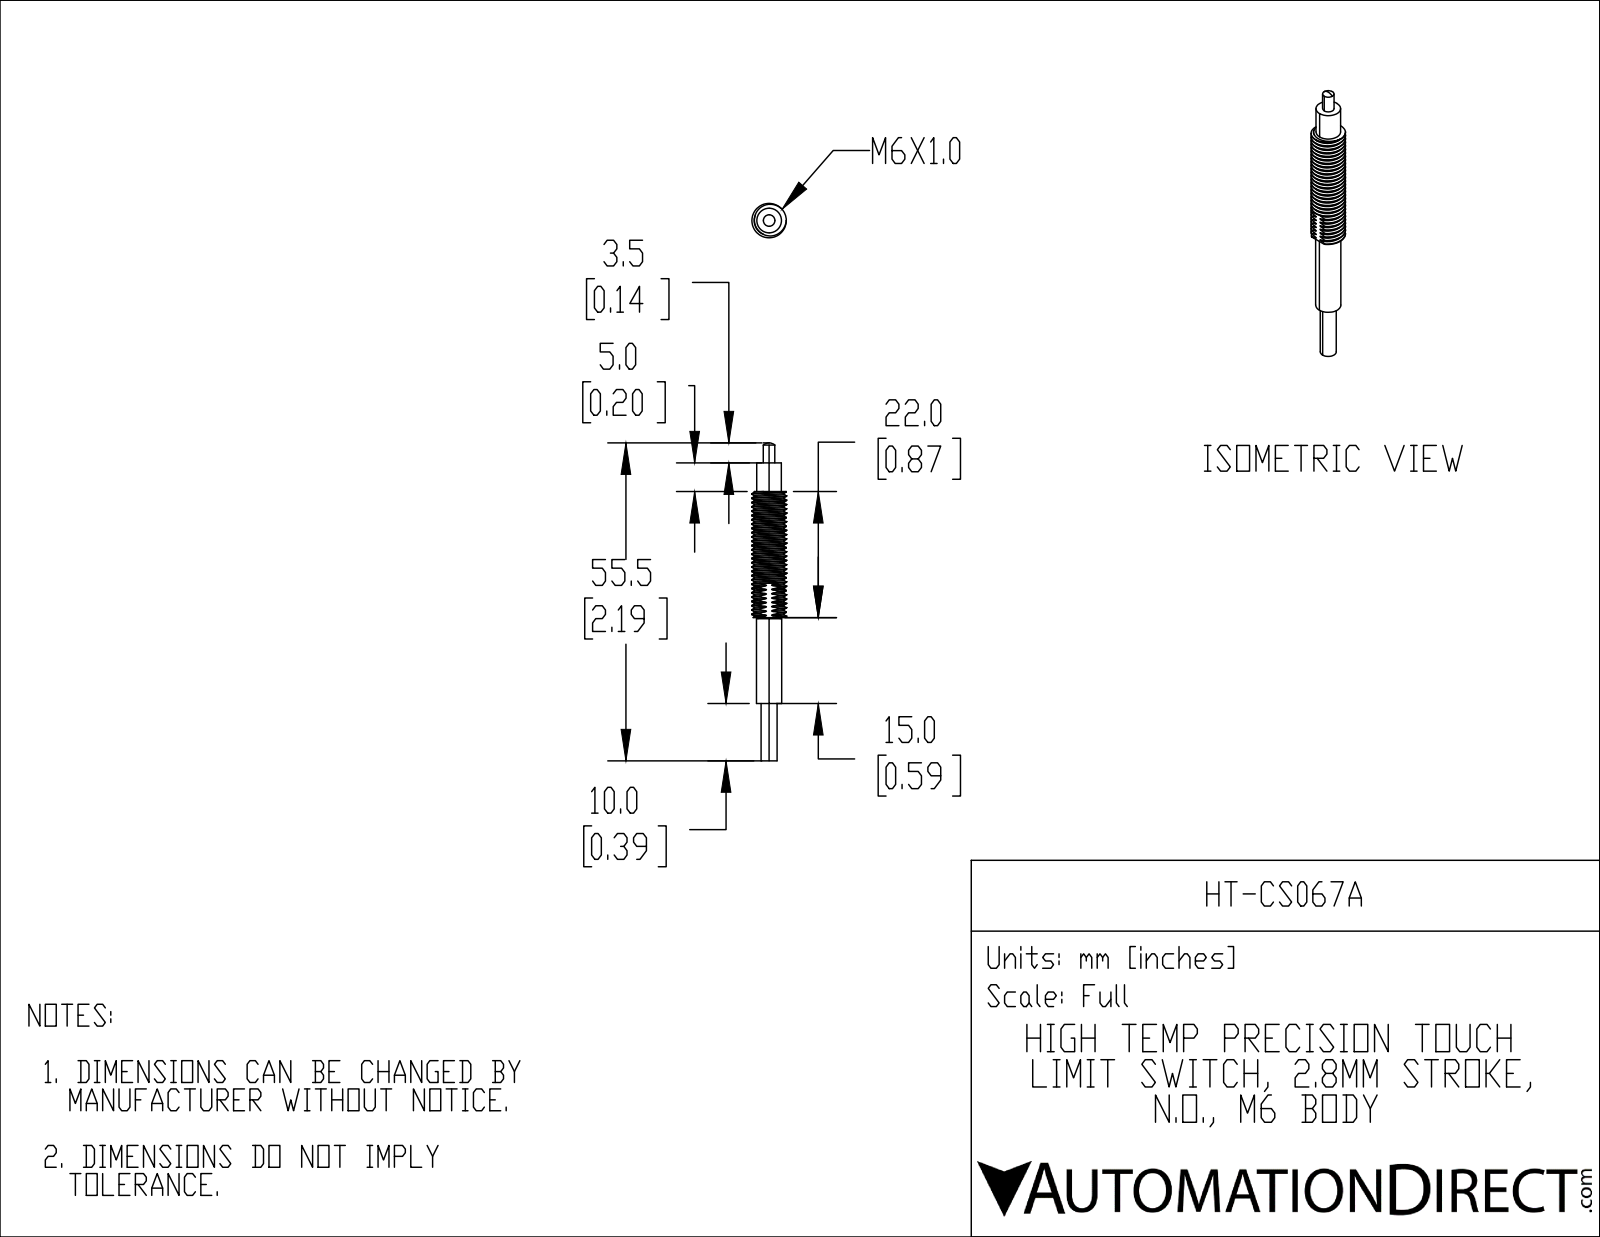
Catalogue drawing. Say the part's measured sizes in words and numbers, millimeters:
The part is named "HT-CS067A". Its 3-D file was written by "SolidWorks 2020 (CONFIG_CONTROL_DESIGN)". It is 1 solid with 133 faces: 10 planar, 70 cylindrical and 53 other. Overall it measures 55.5 by 6 by 6 millimeters. Its volume is 896 cubic millimeters and its surface area 1 058 square millimeters. Round bosses or shafts: 1 of diameter 6, 1 of diameter 4.4, 1 of diameter 4.3, 1 of diameter 3.9, 1 of diameter 2.8, 1 of diameter 2. The main face-to-face distances are 5, 27, 22, 42, 37, 15, 52, 47, 25, 10.
